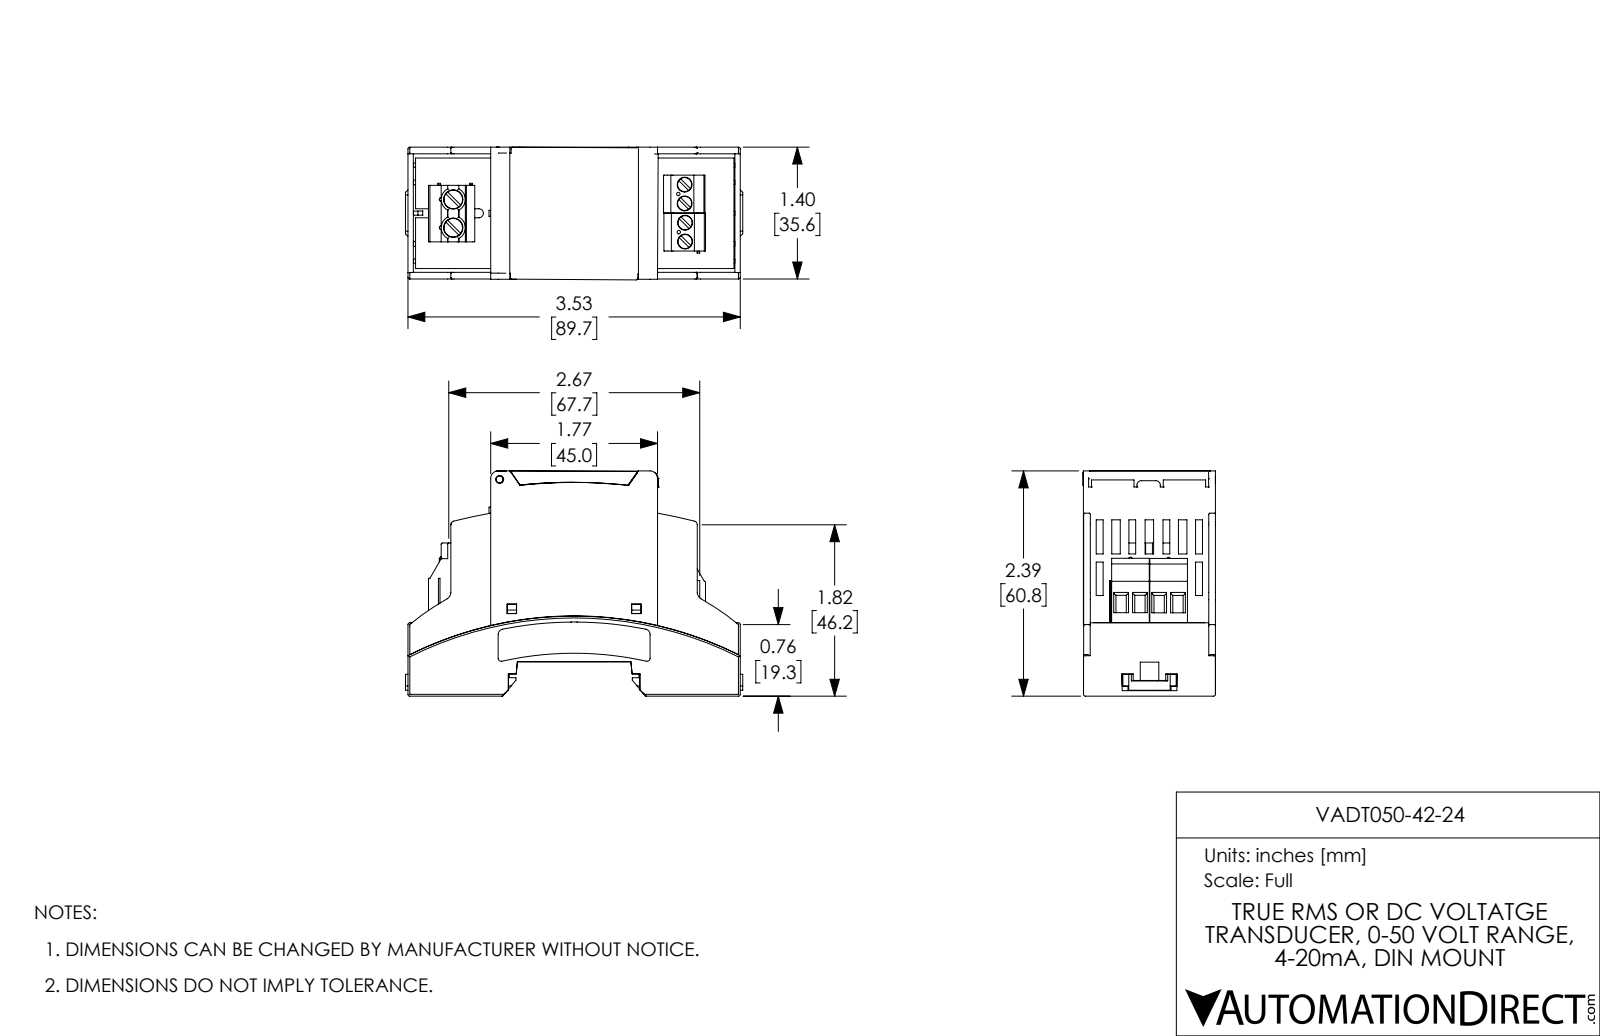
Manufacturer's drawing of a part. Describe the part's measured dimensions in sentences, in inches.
The part is named "VADT050-42-24". Its 3-D file was written by "SolidWorks 2021 (AUTOMOTIVE_DESIGN)". It is 7 solids with 895 faces: 538 planar, 166 cylindrical and 191 other. Overall it measures 4.203 by 2.298 by 1.46 inches. Its volume is 3.182 cubic inches and its surface area 78.38 square inches. Round holes: 4 of diameter 0.157, 2 of diameter 0.205. Round bosses or shafts: 6 of diameter 0.051, 4 of diameter 0.15, 3 of diameter 0.018, 2 of diameter 0.197. Partial cylindrical surfaces (rounded edges, fillets, slot ends): 27 of radius 0.006, 12 of radius 0.039, 11 of radius 0.02, 10 of radius 0.008, 8 of radius 0.026, 6 of radius 0.012, 4 of radius 0.032, 4 of radius 0.04. The main face-to-face distances are 1.435, 0.064, 0.437, 0.501, 1.279, 1.249, 0.266, 0.703, 0.767, 0.771. The hole center spacings are 0.2, 0.4, 2.467, 0.375, 0.6, 2.468, 2.469, 2.482.
